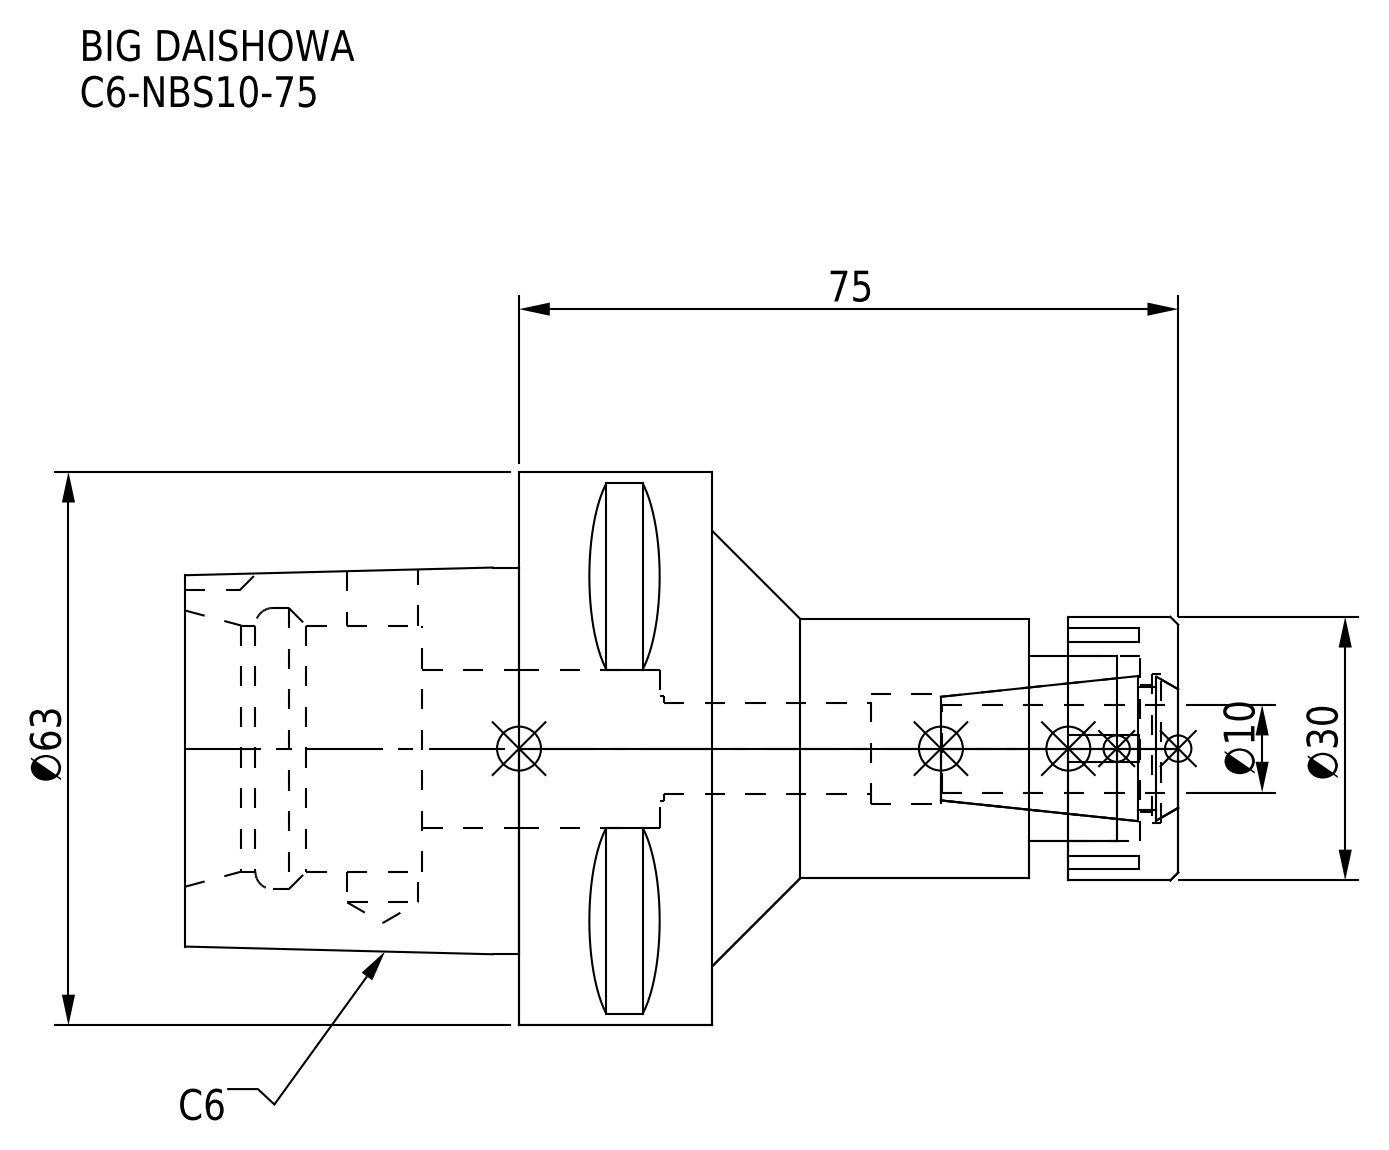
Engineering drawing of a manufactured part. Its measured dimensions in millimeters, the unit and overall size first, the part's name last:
Units: millimetres
Overall size (bounding box): 113 × 63 × 63
Round holes (diameter × count): ⌀8.1 ×1, ⌀10.4 ×1, ⌀12 ×1, ⌀12.5 ×1, ⌀14.5 ×1, ⌀17 ×1, ⌀18 ×1, ⌀21 ×1, ⌀28 ×1, ⌀32 ×1
Round bosses / shafts (diameter × count): ⌀63 ×1, ⌀30 ×1, ⌀29.5 ×1
Partial cylindrical surfaces — rounded edges, fillets, slot ends (radius × count): R5 ×1
Main face-to-face distances: 22, 27, 60, 38, 53, 75, 113, 33, 86, 11
Volume: 129 121 mm³ · Surface area: 28 741 mm²
Bodies: 2 solids, 112 faces (61 planar, 33 cylindrical, 18 other)
Part name (STEP PRODUCT): NBN10_1.stp; C6-NBS10-75_1.stp; DXF_TEMP_ASSY_ASM_4_ASM.stp; C6-NBS10-75-FreeParts (+3 more)
STEP written by: SolidWorks 2019 (CONFIG_CONTROL_DESIGN)
